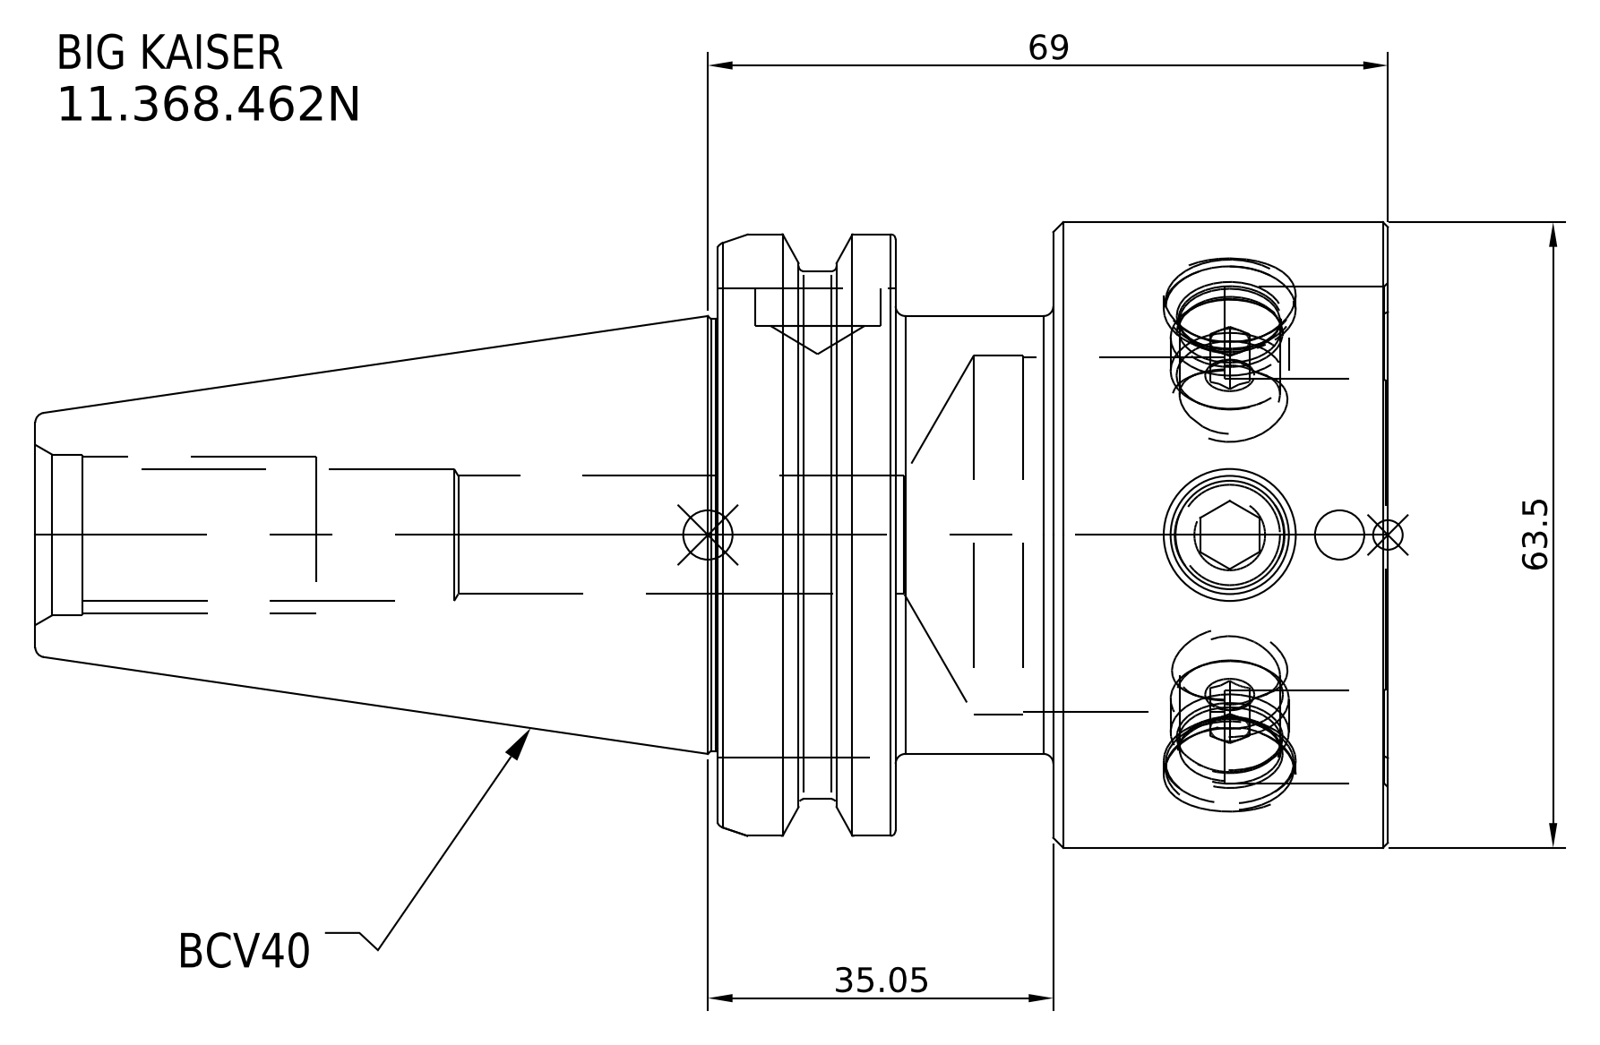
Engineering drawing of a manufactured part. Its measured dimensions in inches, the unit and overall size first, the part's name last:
Units: inches
Overall size (bounding box): 5.404 × 2.5 × 2.5
Round bosses / shafts (diameter × count): ⌀2.5 ×1, ⌀2.491 ×1, ⌀2.219 ×1, ⌀1.75 ×1
Main face-to-face distances: 2.592, 1.967, 0.625, 1.337, 0.63, 1.255, 5.404, 4.067, 3.437, 2.812
Volume: 15.19 in³ · Surface area: 45.4 in²
Bodies: 1 solid, 16 faces (7 planar, 6 cylindrical, 3 other)
Part name (STEP PRODUCT): 11.368.462N
STEP written by: SolidWorks 2021 (CONFIG_CONTROL_DESIGN)
